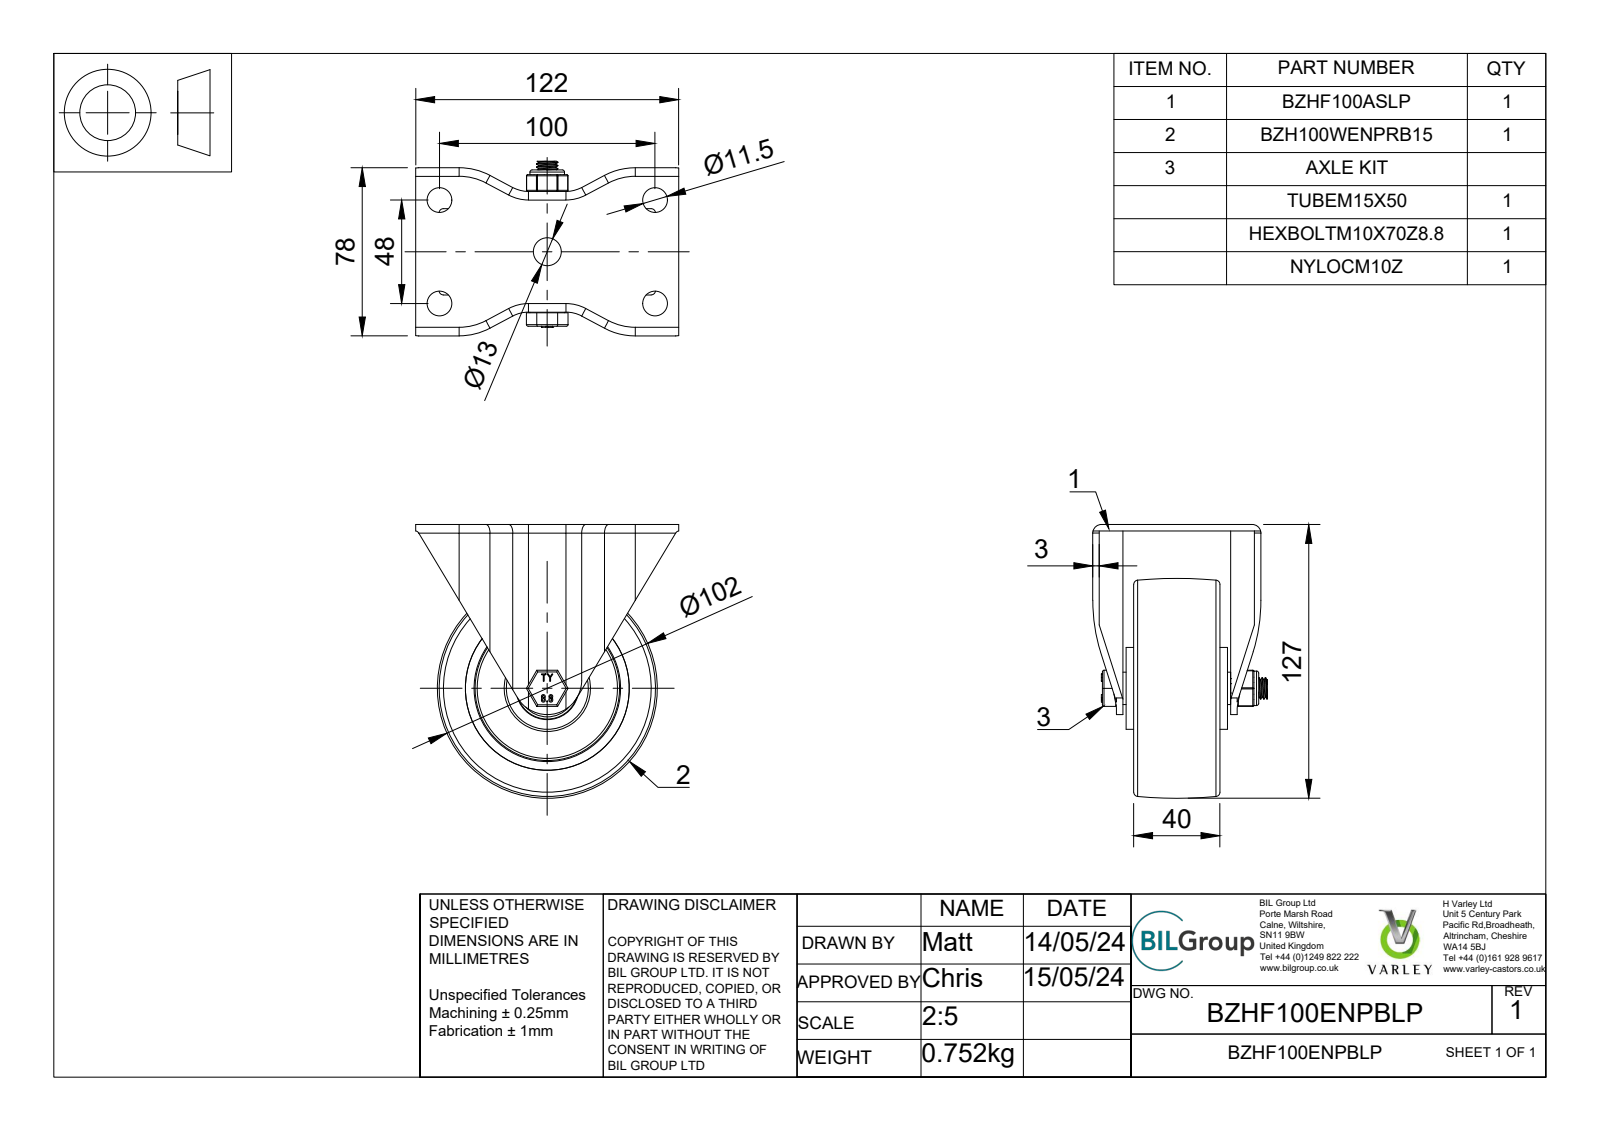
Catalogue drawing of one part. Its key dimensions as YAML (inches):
part_name: "BZHF100ENPBLP v3; BZHF100ASLP - 50 v1; ZINC PLATED PRESSED STEEL BRACKET; BZH100WENPRB15 v1 (+7 more)"
step_written_by: "Autodesk Translation Framework v13.14.0.145 (AUTOMOTIVE_DESIGN)"
units: inches
bodies: {solids: 17, faces: 394, planar: 181, cylindrical: 142, other: 71}
overall_size: [5, 4.803, 3.189]
volume: 18.42
surface_area: 193.5
round_holes:
  - {diameter: 0.453, count: 4}
  - {diameter: 0.394, count: 1}
  - {diameter: 0.413, count: 1}
  - {diameter: 0.425, count: 1}
  - {diameter: 0.472, count: 1}
  - {diameter: 0.512, count: 1}
  - {diameter: 0.61, count: 1}
  - {diameter: 0.925, count: 1}
  - {diameter: 0.945, count: 1}
  - {diameter: 1.142, count: 1}
  - {diameter: 2.992, count: 1}
round_bosses_or_shafts:
  - {diameter: 0.157, count: 8}
  - {diameter: 1.496, count: 1}
  - {diameter: 1.122, count: 1}
  - {diameter: 0.886, count: 1}
  - {diameter: 0.63, count: 1}
  - {diameter: 0.591, count: 1}
  - {diameter: 0.388, count: 1}
  - {diameter: 0.32, count: 1}
partial_cylinders:
  - {radius: 0.02, count: 18}
  - {radius: 0.157, count: 8}
  - {radius: 0.03, count: 6}
  - {radius: 0.61, count: 4}
  - {radius: 1.201, count: 4}
  - {radius: 0.079, count: 2}
  - {radius: 0.364, count: 1}
  - {radius: 0.63, count: 1}
face_to_face_distances: [0.118, 0.315, 1.772, 0.197, 0.709, 0.906, 1.063, 0.866, 1.575, 2.205]
hole_center_spacings: [2.183, 1.89, 3.937, 4.367]
